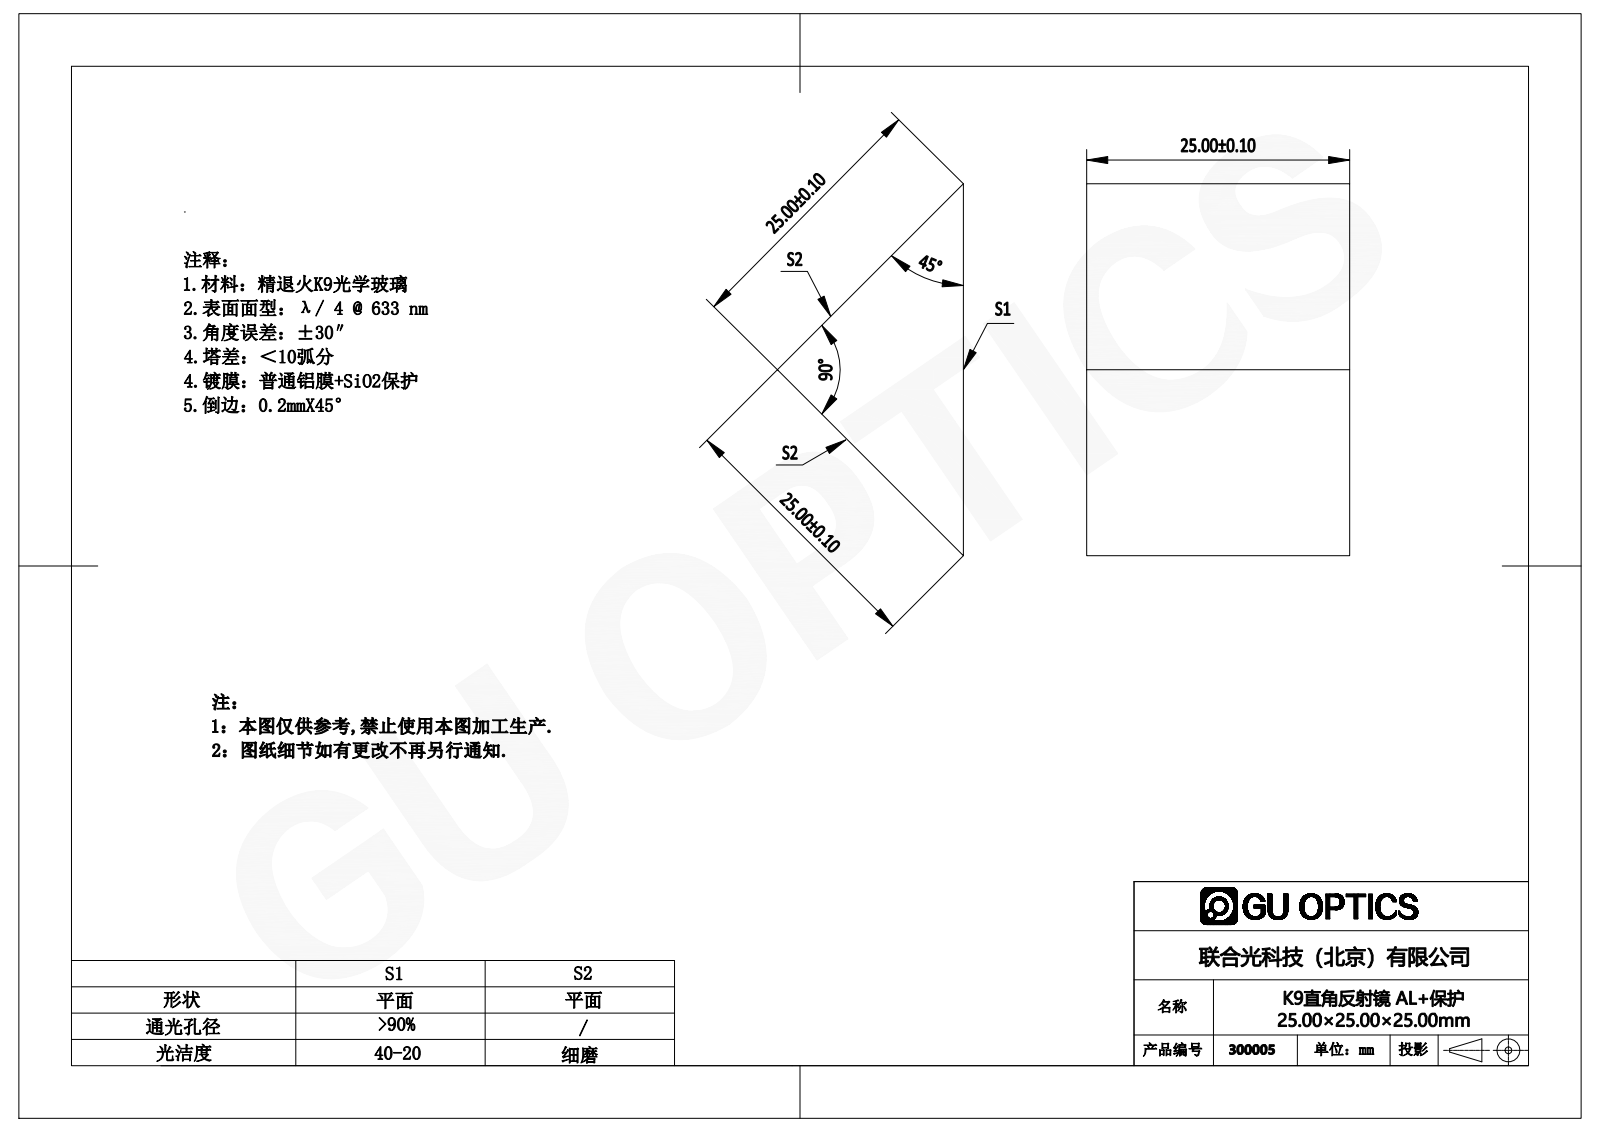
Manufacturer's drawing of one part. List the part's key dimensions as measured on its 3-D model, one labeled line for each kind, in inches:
Part name (STEP PRODUCT): 300005
STEP written by: SolidWorks 2016 (AUTOMOTIVE_DESIGN)
Units: inches
Bodies: 1 solid, 5 faces (5 planar, 0 cylindrical, 0 other)
Overall size (bounding box): 1.392 × 0.984 × 0.696
Volume: 0.477 in³ · Surface area: 4.276 in²
Main face-to-face distances: 0.984
